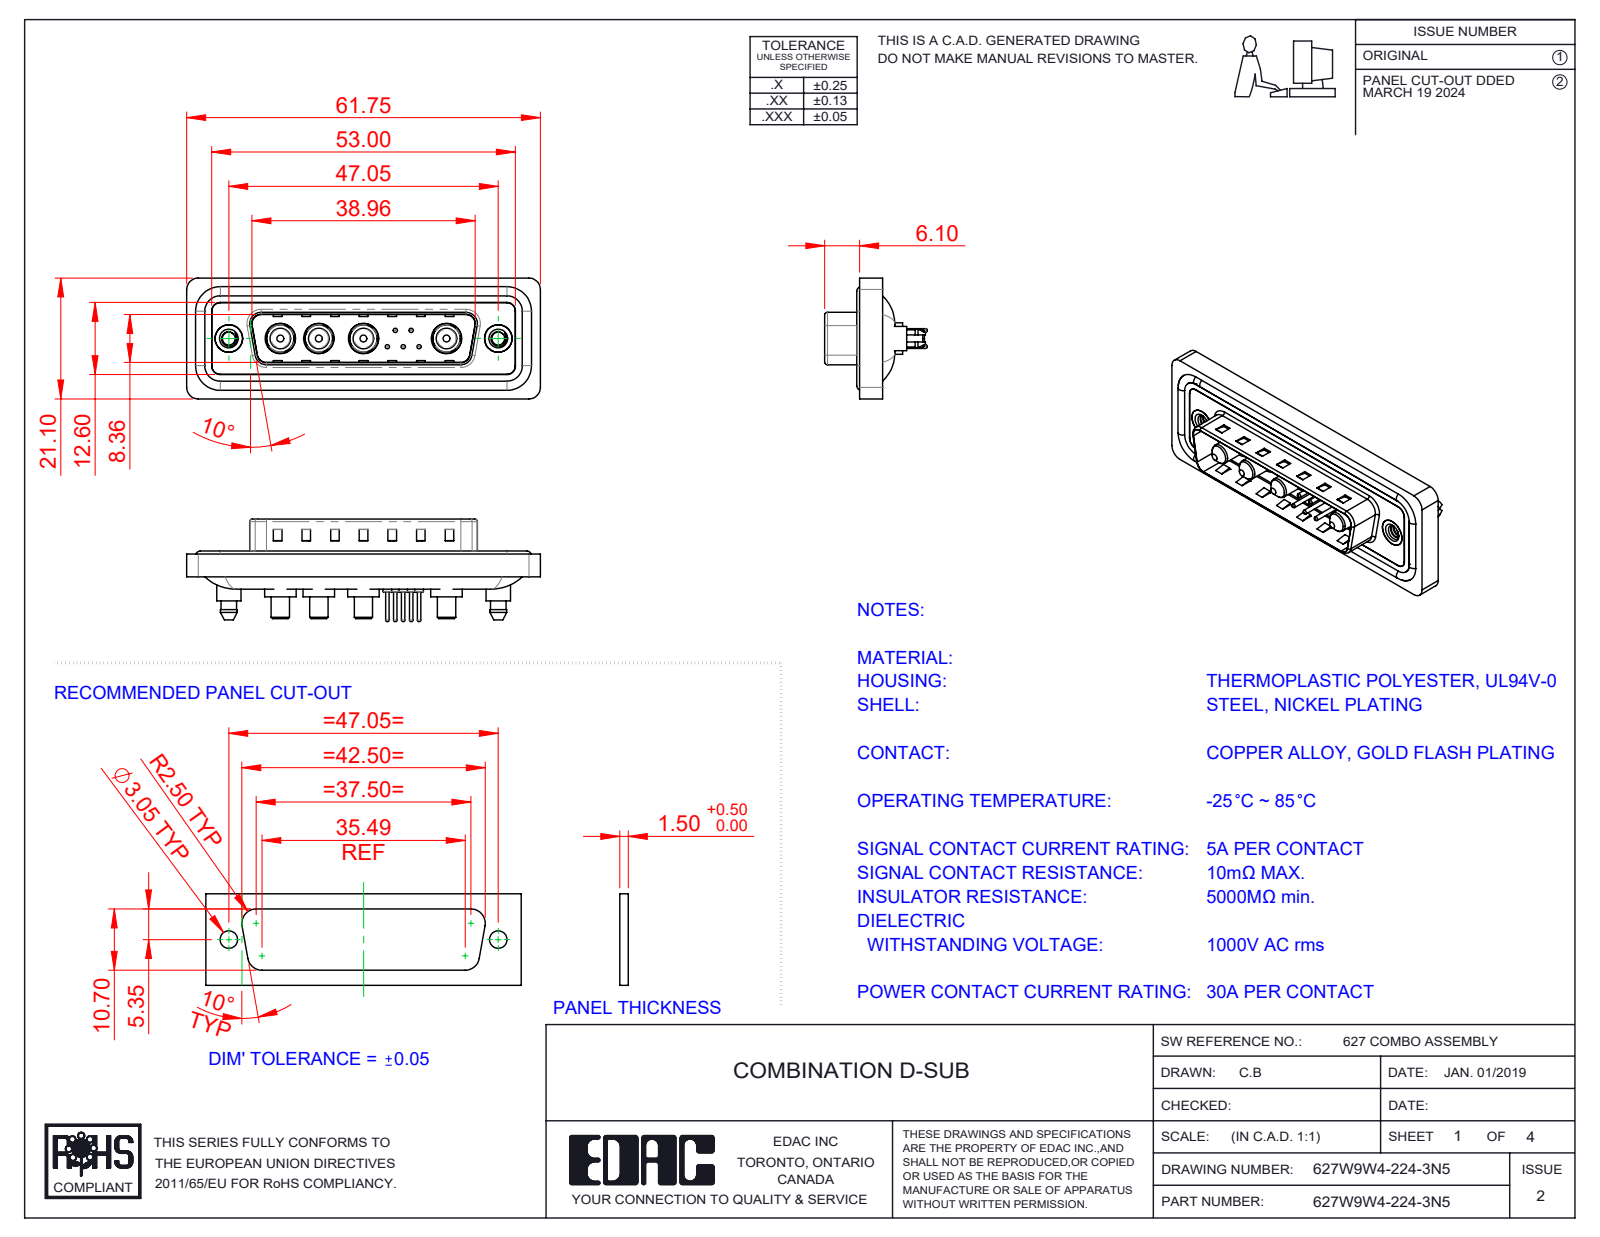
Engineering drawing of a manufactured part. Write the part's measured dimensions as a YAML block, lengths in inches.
part_name: "Power Pin_30A S; 627Combo Contact Row 1_24; 627Combo Contact Row 2_24; 627Combo Waterproof Housing_25 Contacts (+5 more)"
step_written_by: "SolidWorks 2023 (CONFIG_CONTROL_DESIGN)"
units: inches
bodies: {solids: 20, faces: 874, planar: 300, cylindrical: 366, other: 208}
overall_size: [2.431, 0.831, 0.705]
volume: 0.462
surface_area: 18.89
round_holes:
  - {diameter: 0.03, count: 5}
  - {diameter: 0.063, count: 5}
  - {diameter: 0.079, count: 5}
  - {diameter: 0.191, count: 4}
  - {diameter: 0.209, count: 4}
  - {diameter: 0.089, count: 2}
  - {diameter: 0.157, count: 2}
  - {diameter: 0.189, count: 2}
  - {diameter: 0.197, count: 2}
round_bosses_or_shafts:
  - {diameter: 0.059, count: 5}
  - {diameter: 0.024, count: 5}
  - {diameter: 0.217, count: 4}
  - {diameter: 0.205, count: 4}
  - {diameter: 0.187, count: 4}
  - {diameter: 0.148, count: 4}
  - {diameter: 0.142, count: 4}
  - {diameter: 0.126, count: 4}
partial_cylinders:
  - {radius: 0.059, count: 24}
  - {radius: 0.079, count: 18}
  - {radius: 0.063, count: 10}
  - {radius: 0.02, count: 8}
  - {radius: 0.01, count: 4}
  - {radius: 0.024, count: 4}
  - {radius: 0.026, count: 4}
  - {radius: 0.035, count: 4}
face_to_face_distances: [0.016, 0.059, 0.043, 0.02, 0.122, 0.063, 0.114, 0.032, 0.377, 0.222]
hole_center_spacings: [0.124, 0.109, 0.198, 0.571, 0.109, 0.173, 0.174, 0.197]
